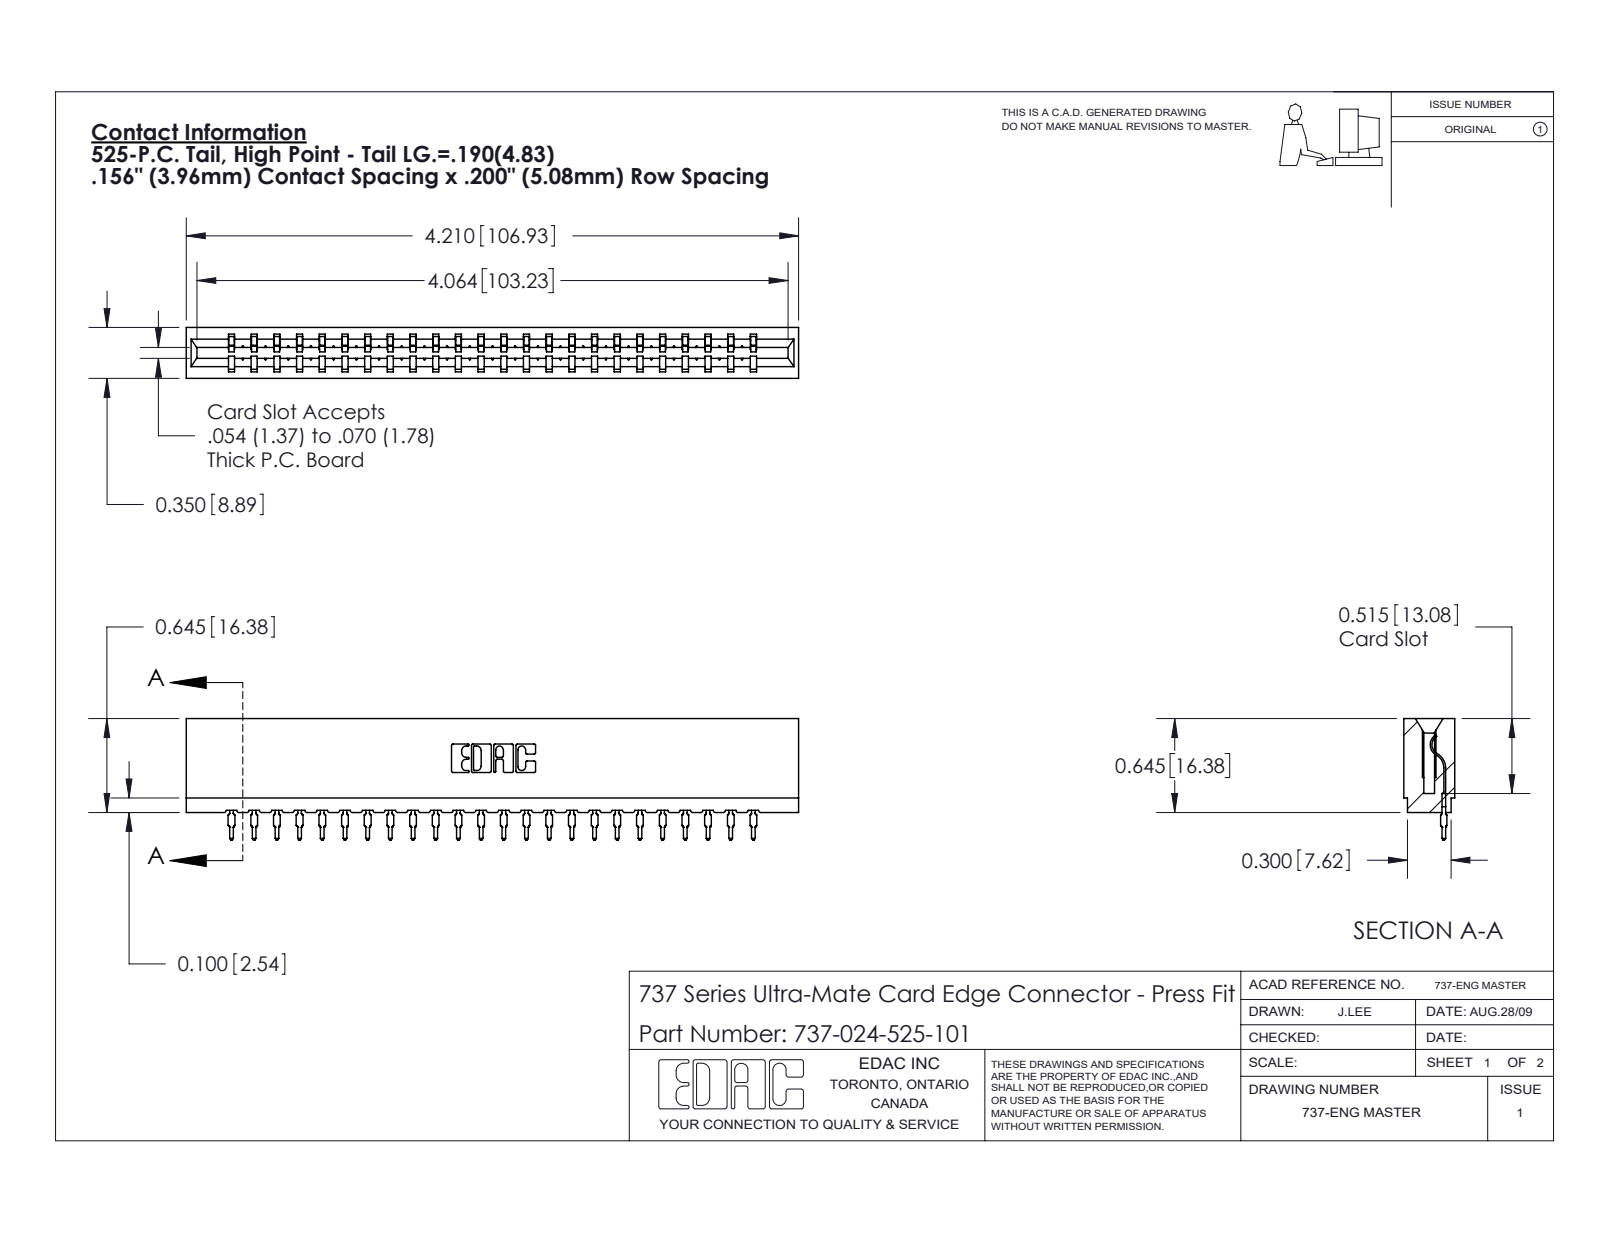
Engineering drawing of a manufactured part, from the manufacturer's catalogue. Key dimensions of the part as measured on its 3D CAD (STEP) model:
Part name (STEP PRODUCT): 745-292-001_525; 737 Part_Insulator Option - 01; 737-024-525-101
STEP written by: SolidWorks 2020 (CONFIG_CONTROL_DESIGN)
Units: inches
Bodies: 25 solids, 2806 faces (1686 planar, 496 cylindrical, 624 other)
Overall size (bounding box): 4.21 × 0.836 × 0.35
Volume: 0.637 in³ · Surface area: 21.13 in²
Partial cylindrical surfaces — rounded edges, fillets, slot ends (radius × count): R0.015 ×48, R0.021 ×48, R0.01 ×22, R0.007 ×6, R0.031 ×6, R0.005 ×4, R0.011 ×4, R0.026 ×3
Main face-to-face distances: 0.138, 0.212, 0.35, 0.074, 0.624, 0.156, 0.045, 0.305, 0.093, 0.167
